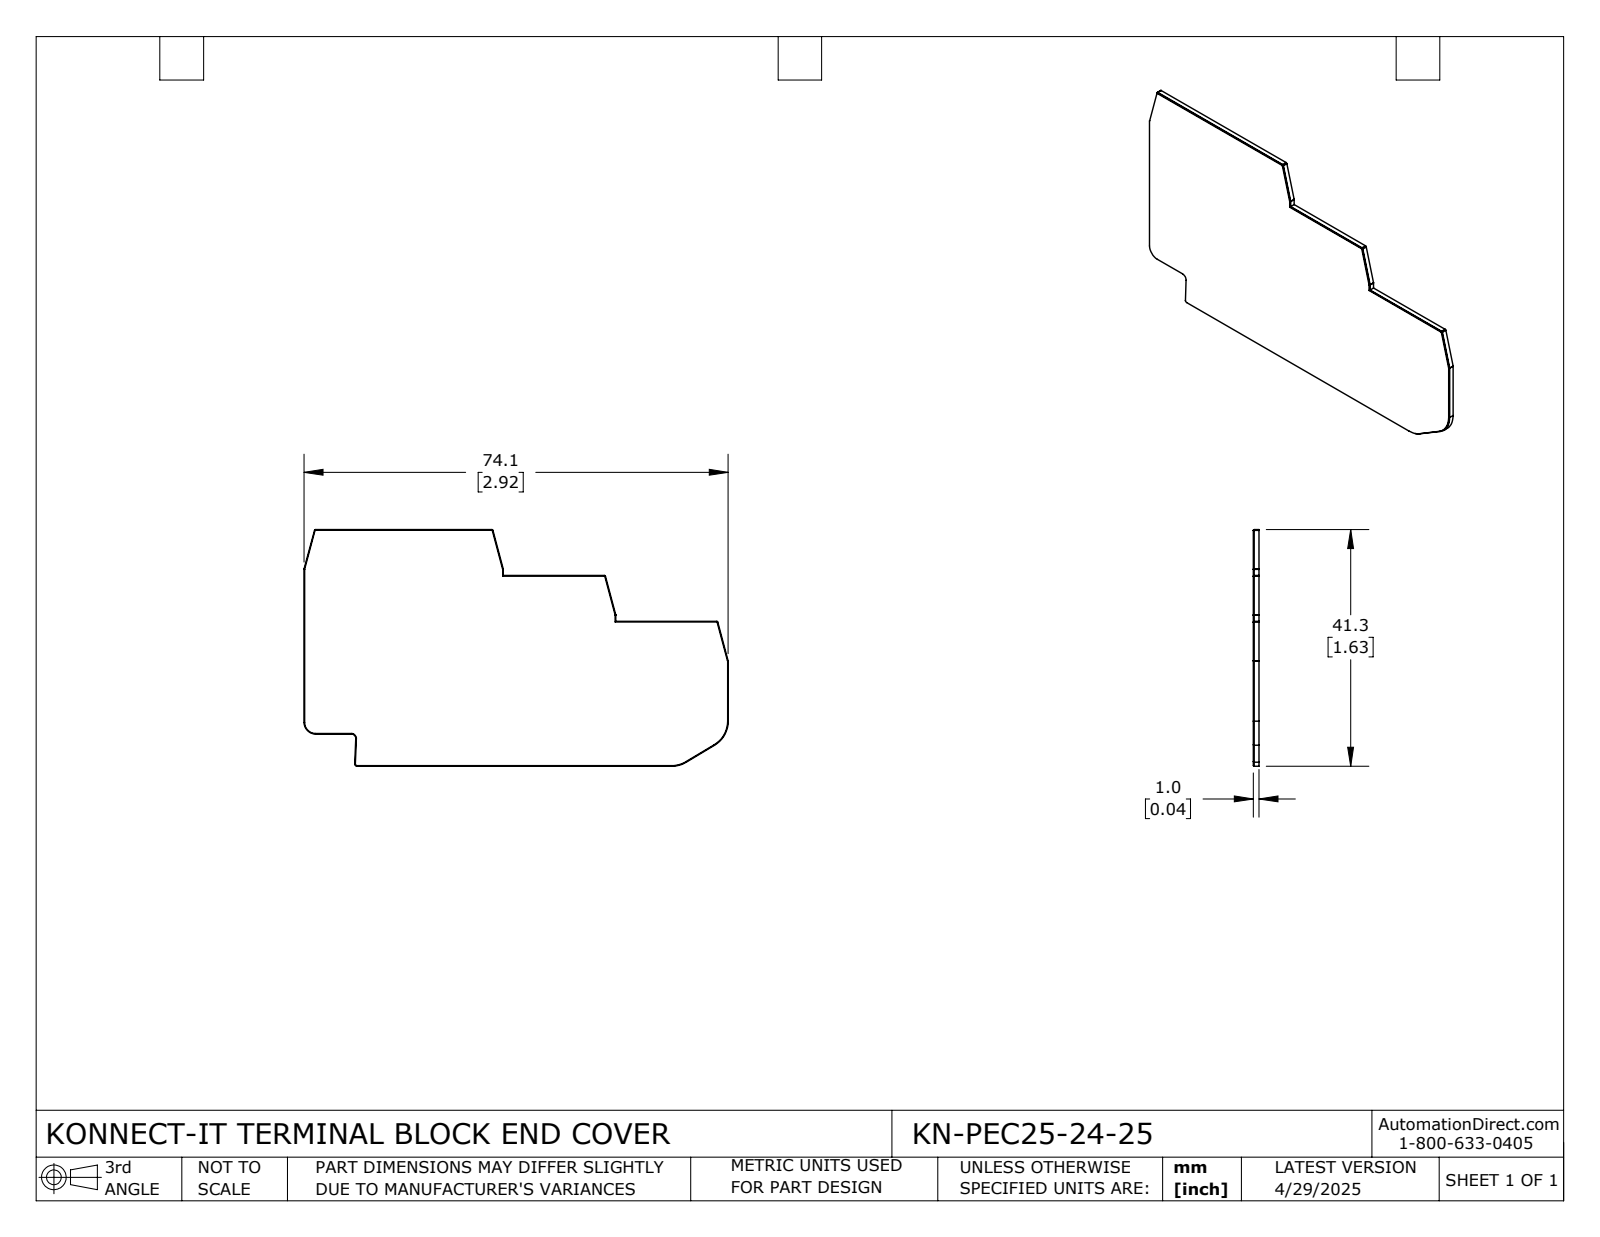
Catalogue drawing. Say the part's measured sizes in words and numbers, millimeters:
The part is named "KN-PEC25-24-25". Its 3-D file was written by "SolidWorks 2024 (CONFIG_CONTROL_DESIGN)". It is 1 solid with 62 faces: 35 planar, 27 cylindrical and 0 other. Overall it measures 74.05 by 41.3 by 1 millimeters. Its volume is 2 485 cubic millimeters and its surface area 5 194 square millimeters. Partial cylindrical surfaces (rounded edges, fillets, slot ends): 8 of radius 0.1, 8 of radius 0.2, 2 of radius 4.9, 1 of radius 0.3, 1 of radius 0.4, 1 of radius 0.78, 1 of radius 0.88, 1 of radius 1.9. The main face-to-face distances are 1, 41.31, 0.85, 16.01, 8, 8.01, 25.3, 33.3, 41.21, 25.2.
